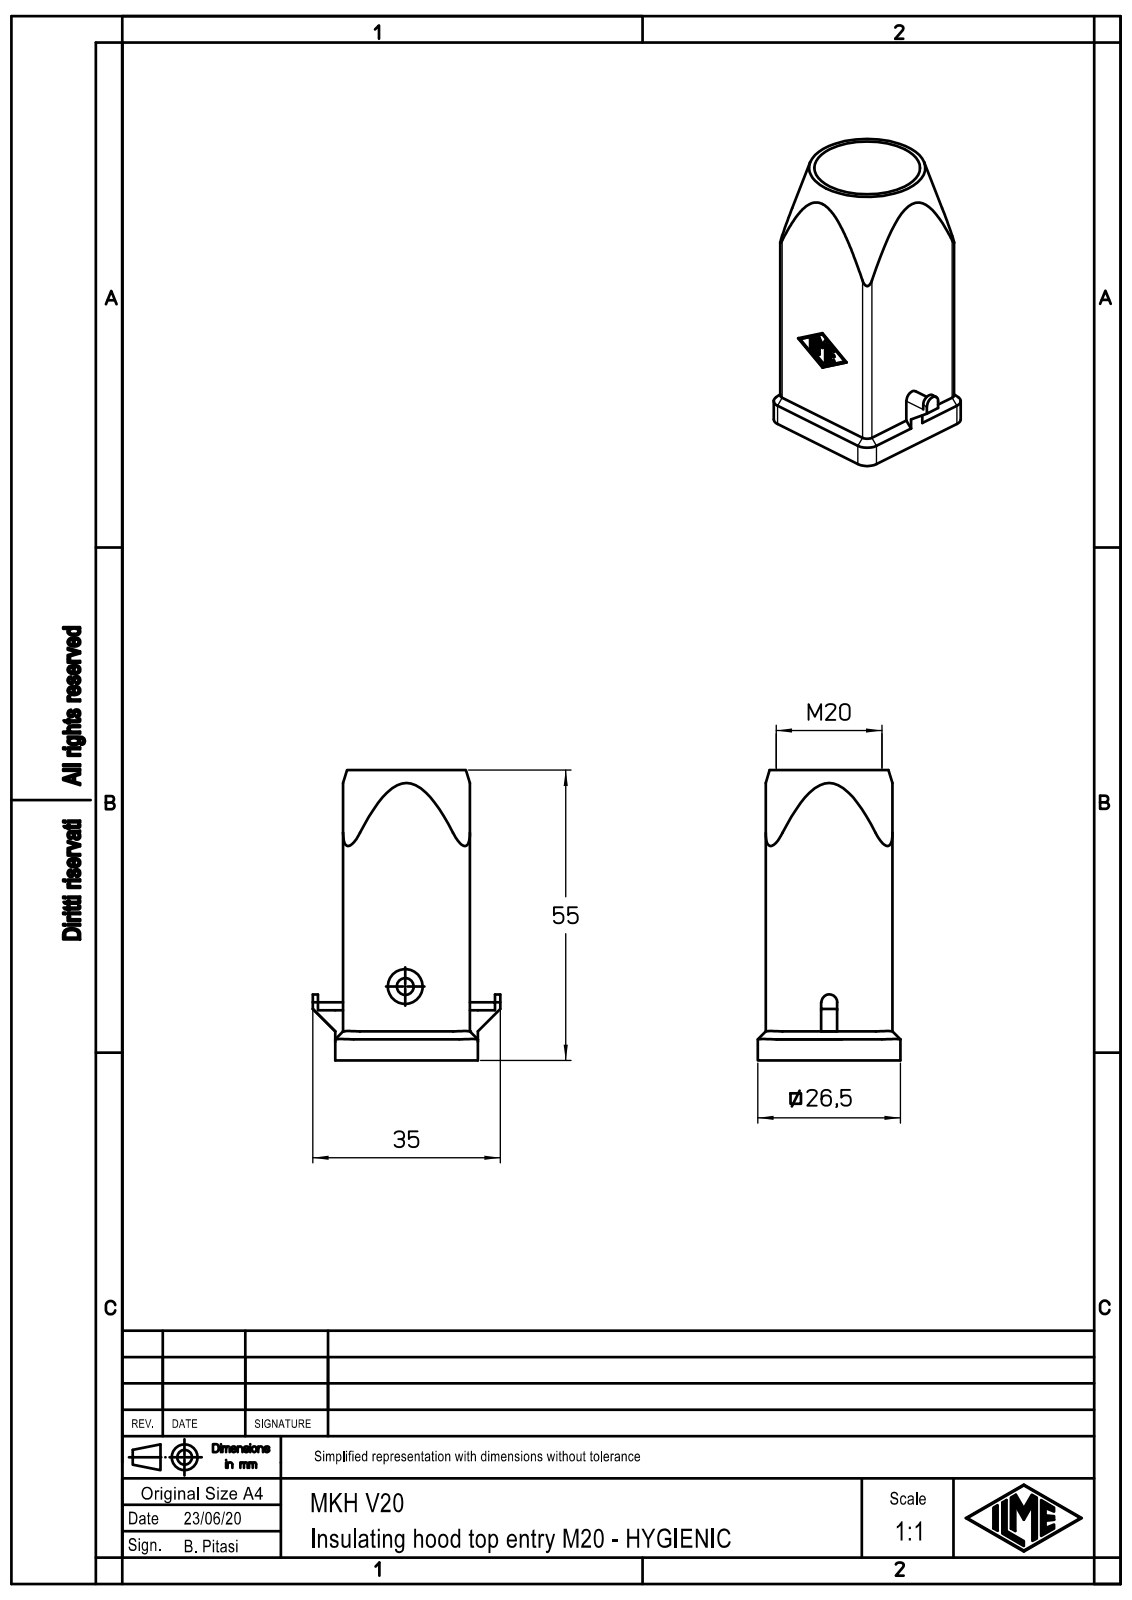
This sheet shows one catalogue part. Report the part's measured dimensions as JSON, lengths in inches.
{"part_name": "MKH V20", "step_written_by": "Creo Elements/Direct Modeling 20.1B 02-Apr-2019 (C) Parametric Technology GmbH (AUTOMOTIVE_DESIGN)", "units": "inches", "bodies": {"solids": 1, "faces": 126, "planar": 77, "cylindrical": 40, "other": 9}, "overall_size": [2.165, 1.378, 1.043], "volume_in3": 0.481, "surface_area_in2": 16.23, "round_holes": [[0.13, 1], [0.591, 1], [0.787, 1]], "partial_cylinders_radius": [[0.01, 14], [0.069, 8], [0.049, 4], [0.098, 4], [0.059, 2]], "face_to_face_distances": [0.049, 0.896, 0.945, 0.846, 0.098, 0.994, 0.02, 0.03, 0.069, 0.915]}
